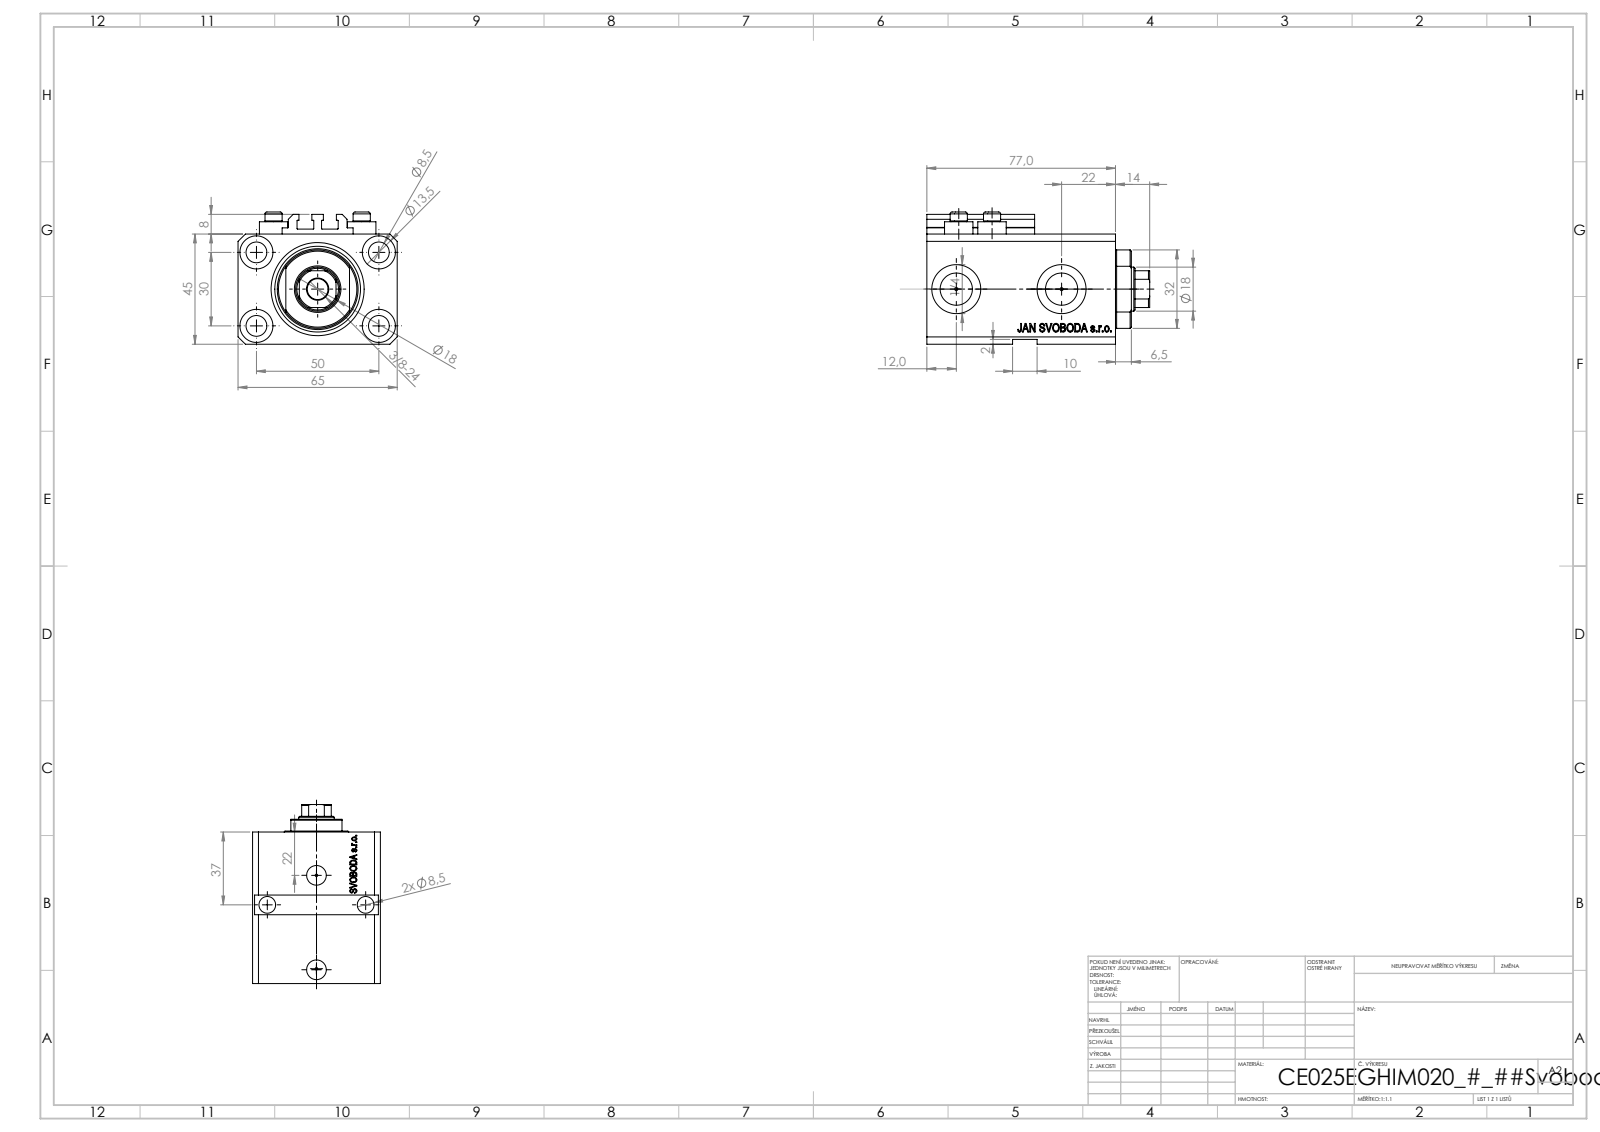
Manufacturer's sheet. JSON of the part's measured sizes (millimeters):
{"part_name": "V250CE_C_VCP; ALLEN BOLT V250CE; V250CE_E_Body; V250CE_VC_E", "step_written_by": "SolidWorks 2019 (CONFIG_CONTROL_DESIGN)", "units": "millimeters", "bodies": {"solids": 8, "faces": 1067, "planar": 511, "cylindrical": 126, "other": 430}, "overall_size": [91, 65, 54], "volume_mm3": 199775, "surface_area_mm2": 59185, "round_holes": [[8.5, 7], [1.25, 4], [4, 4], [13.5, 4], [10, 2], [13.16, 2], [20, 2], [18, 1], [25, 1], [38, 1]], "round_bosses_or_shafts": [[11.6, 4], [7, 4]], "partial_cylinders_radius": [[0.2, 10], [8.5, 1], [16, 1]], "face_to_face_distances": [45, 65, 63, 14, 77, 2, 6.9, 56.1, 70.1, 47], "hole_center_spacings": [29.15, 50, 13.6, 15.12, 18.81, 18.97, 26.22, 26.61]}
